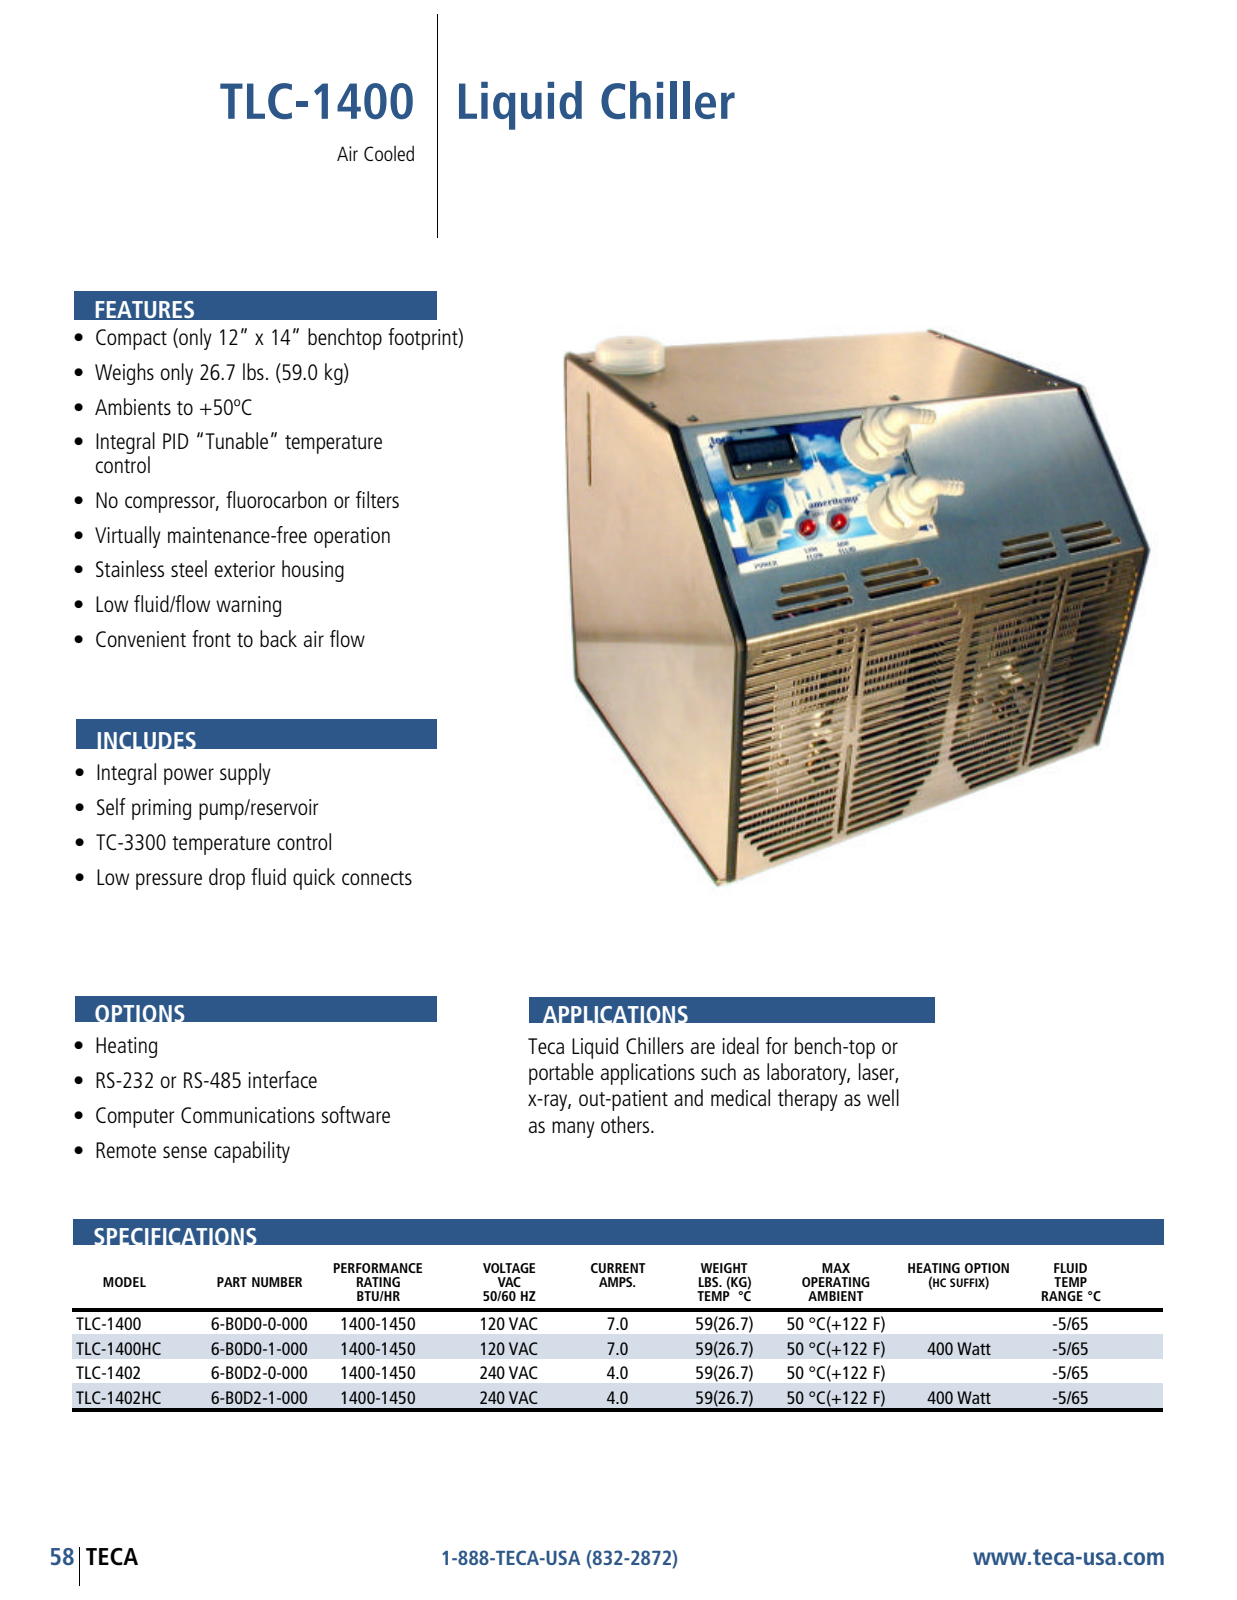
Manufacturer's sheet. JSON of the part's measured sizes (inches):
{"part_name": "TLC-1400", "step_written_by": "SolidWorks 2016 (CONFIG_CONTROL_DESIGN)", "units": "inches", "bodies": {"solids": 0, "faces": 4380, "planar": 3170, "cylindrical": 981, "other": 229}, "overall_size": [16.334, 14.342, 13.058], "round_holes": [[0.156, 68], [0.188, 29], [0.25, 24], [0.13, 13], [0.172, 8], [0.313, 4], [0.625, 3], [0.375, 2], [0.75, 2], [1, 2], [1.2, 2], [1.25, 2]], "round_bosses_or_shafts": [[0.28, 15], [0.187, 5], [0.53, 4], [0.337, 4], [0.163, 4], [0.15, 3], [3, 2], [1.62, 2]], "partial_cylinders_radius": [[0.094, 245], [0.188, 20], [0.125, 16], [0.156, 10], [4.072, 8], [4.74, 8], [0.09, 6], [0.03, 5]], "face_to_face_distances": [0.06, 6, 0.15, 12, 14.18, 6.06, 5.94, 0.3, 0.06, 0.05], "hole_center_spacings": [7.12, 1.43, 7.262, 2.87, 7.264, 7.677, 3.187, 1.42]}
